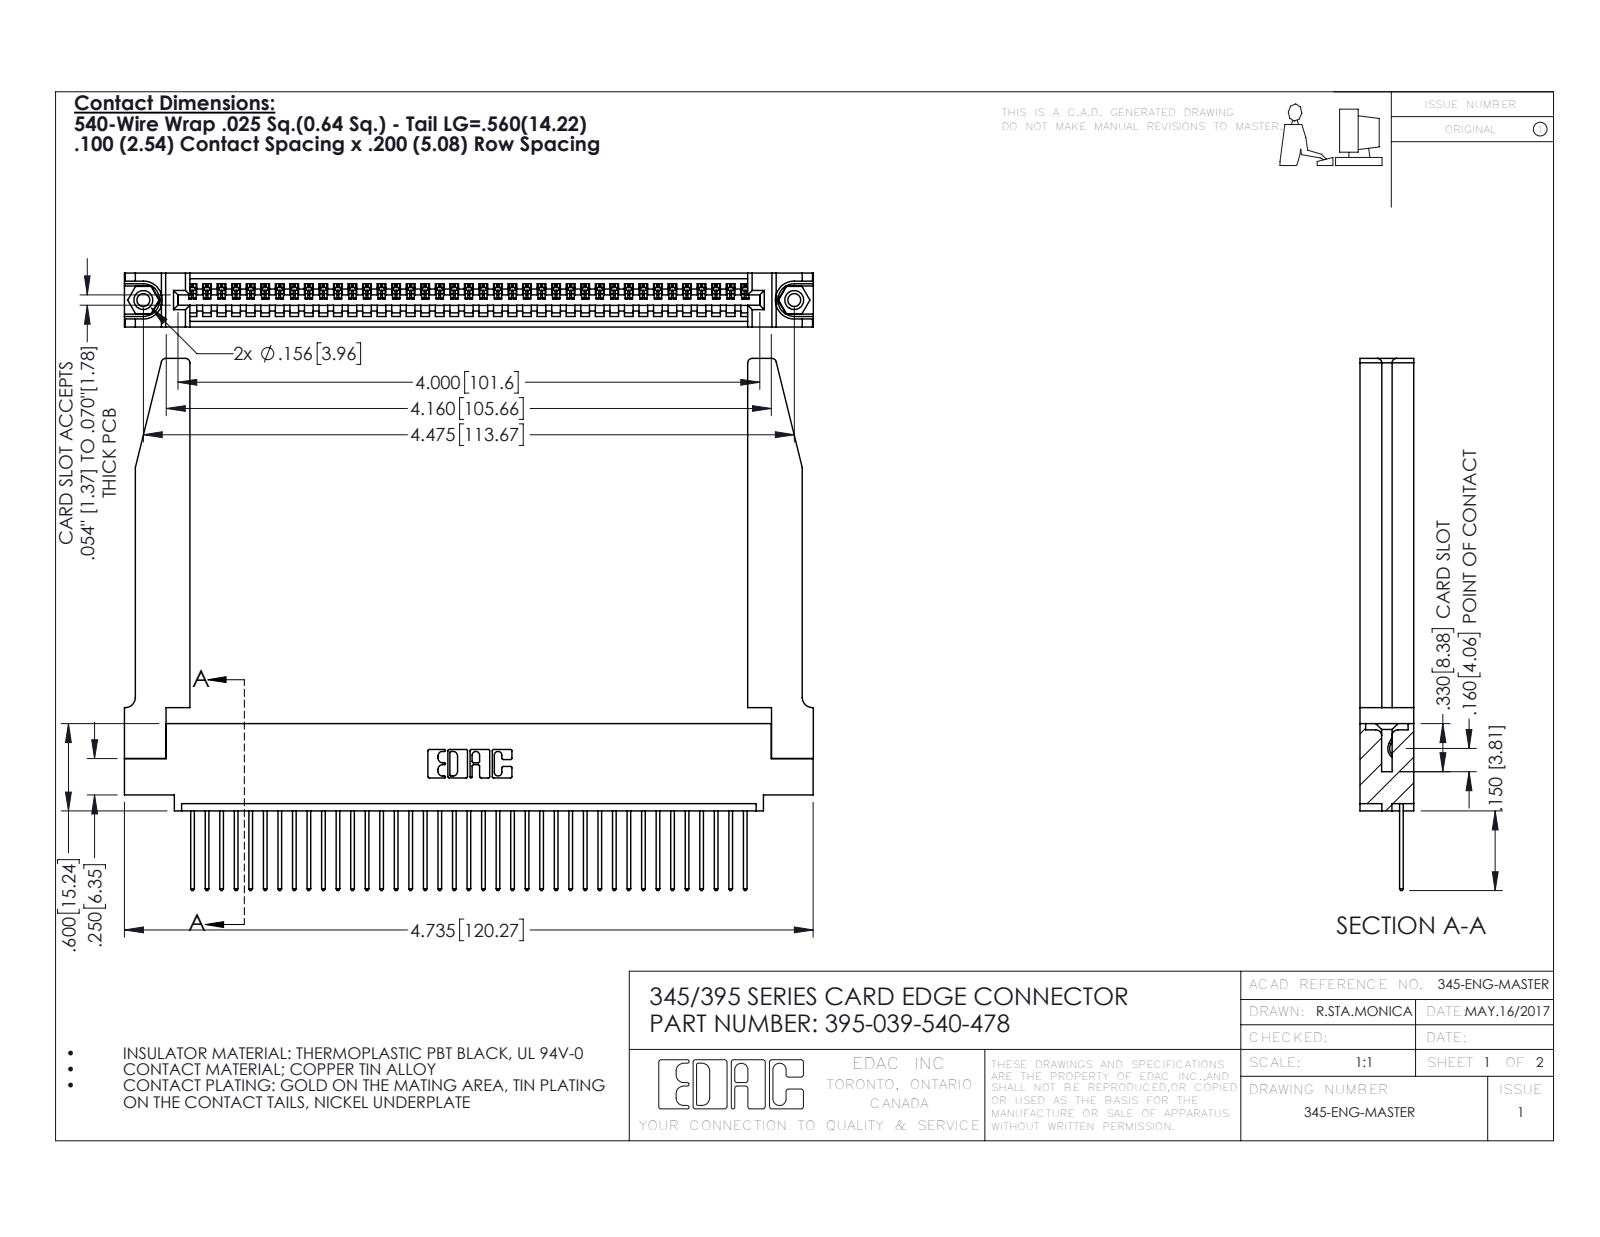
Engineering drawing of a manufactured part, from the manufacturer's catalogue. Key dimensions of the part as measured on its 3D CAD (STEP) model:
Part name (STEP PRODUCT): 395-039-540-478; 345-292-001_345-293-140; 345-250-001_345-250-001-102; 345 Part_0.110 Offset - 0.156 Dia-TH (+1 more)
STEP written by: SolidWorks 2016 (CONFIG_CONTROL_DESIGN)
Units: inches
Bodies: 44 solids, 2626 faces (1786 planar, 788 cylindrical, 52 other)
Overall size (bounding box): 4.736 × 3.657 × 0.37
Volume: 1.169 in³ · Surface area: 34.71 in²
Round holes (diameter × count): ⌀0.089 ×2, ⌀0.125 ×2, ⌀0.156 ×2, ⌀0.064 ×1
Round bosses / shafts (diameter × count): ⌀0.155 ×2
Partial cylindrical surfaces — rounded edges, fillets, slot ends (radius × count): R0.006 ×78, R0.01 ×78, R0.01 ×22, R0.03 ×8, R0.007 ×6, R0.031 ×6, R0.026 ×3, R0.031 ×2
Main face-to-face distances: 0.37, 0.072, 0.298, 0.098, 0.272, 0.025, 0.2, 0.225, 0.148, 0.15
Hole centre spacings: 0.27, 4.239, 4.475
